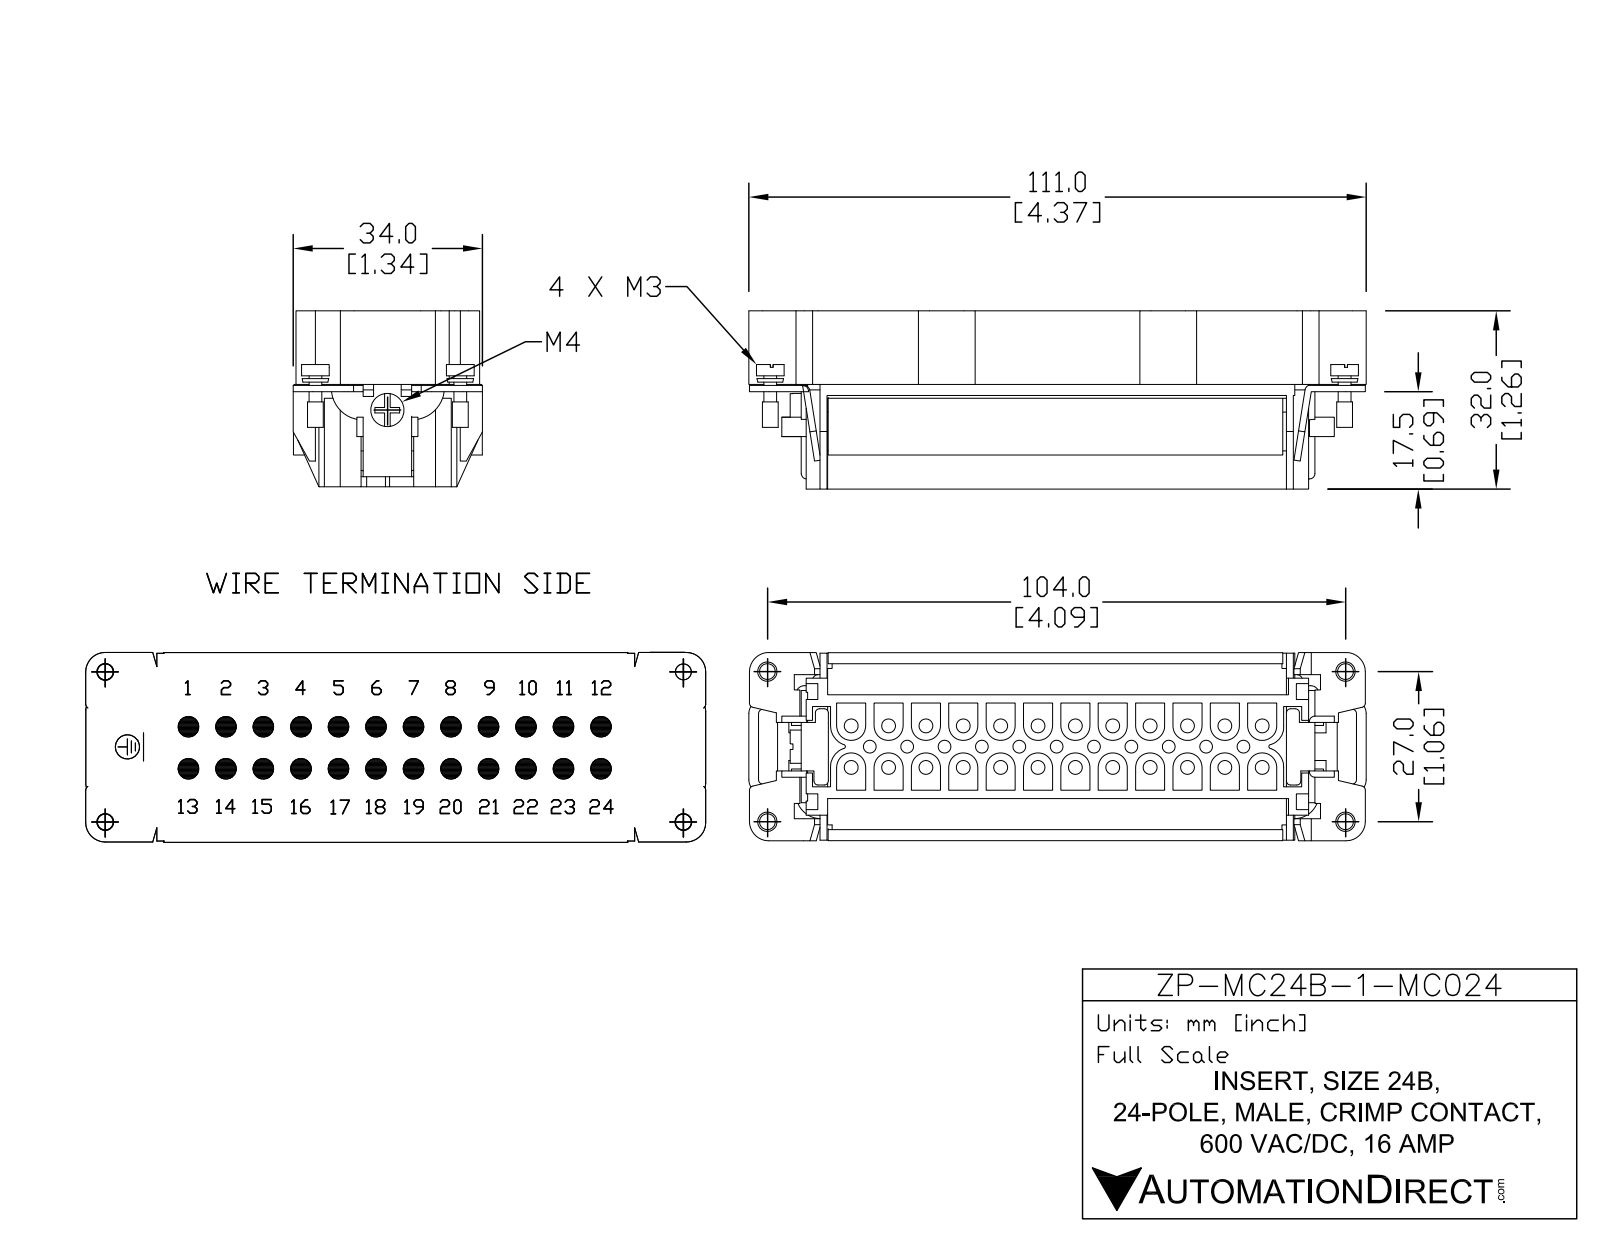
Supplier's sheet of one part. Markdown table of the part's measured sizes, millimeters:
| quantity | value |
| --- | --- |
| part name | ZP-24B-24-MC-INSERT |
| STEP written by | SolidWorks 2011 (AUTOMOTIVE_DESIGN) |
| units | millimeters |
| bodies | 9 solids, 893 faces (607 planar, 258 cylindrical, 28 other) |
| overall size | 111.5 × 34 × 32 |
| volume | 43 063 mm³ |
| surface area | 49 639 mm² |
| round holes (diameter × count) | 2.5 × 24, 4.75 × 12, 2.3 × 11, 3.5 × 4, 3 × 1 |
| round bosses / shafts (diameter × count) | 5 × 4, 2.85 × 4, 2.3 × 4, 6 × 1 |
| partial cylindrical surfaces (radius × count) | 0.75 × 24, 2.62 × 24, 2.62 × 24, 1 × 11, 0.25 × 10, 2 × 10, 2.5 × 4, 2.5 × 4 |
| main face-to-face distances | 2.5, 1.75, 12, 7, 5, 13.5, 3.63, 1.88, 20.62, 1.5 |
| hole center spacings | 6.75, 13.5, 20.25, 27, 10.09, 33.75, 15.44, 21.59 |
